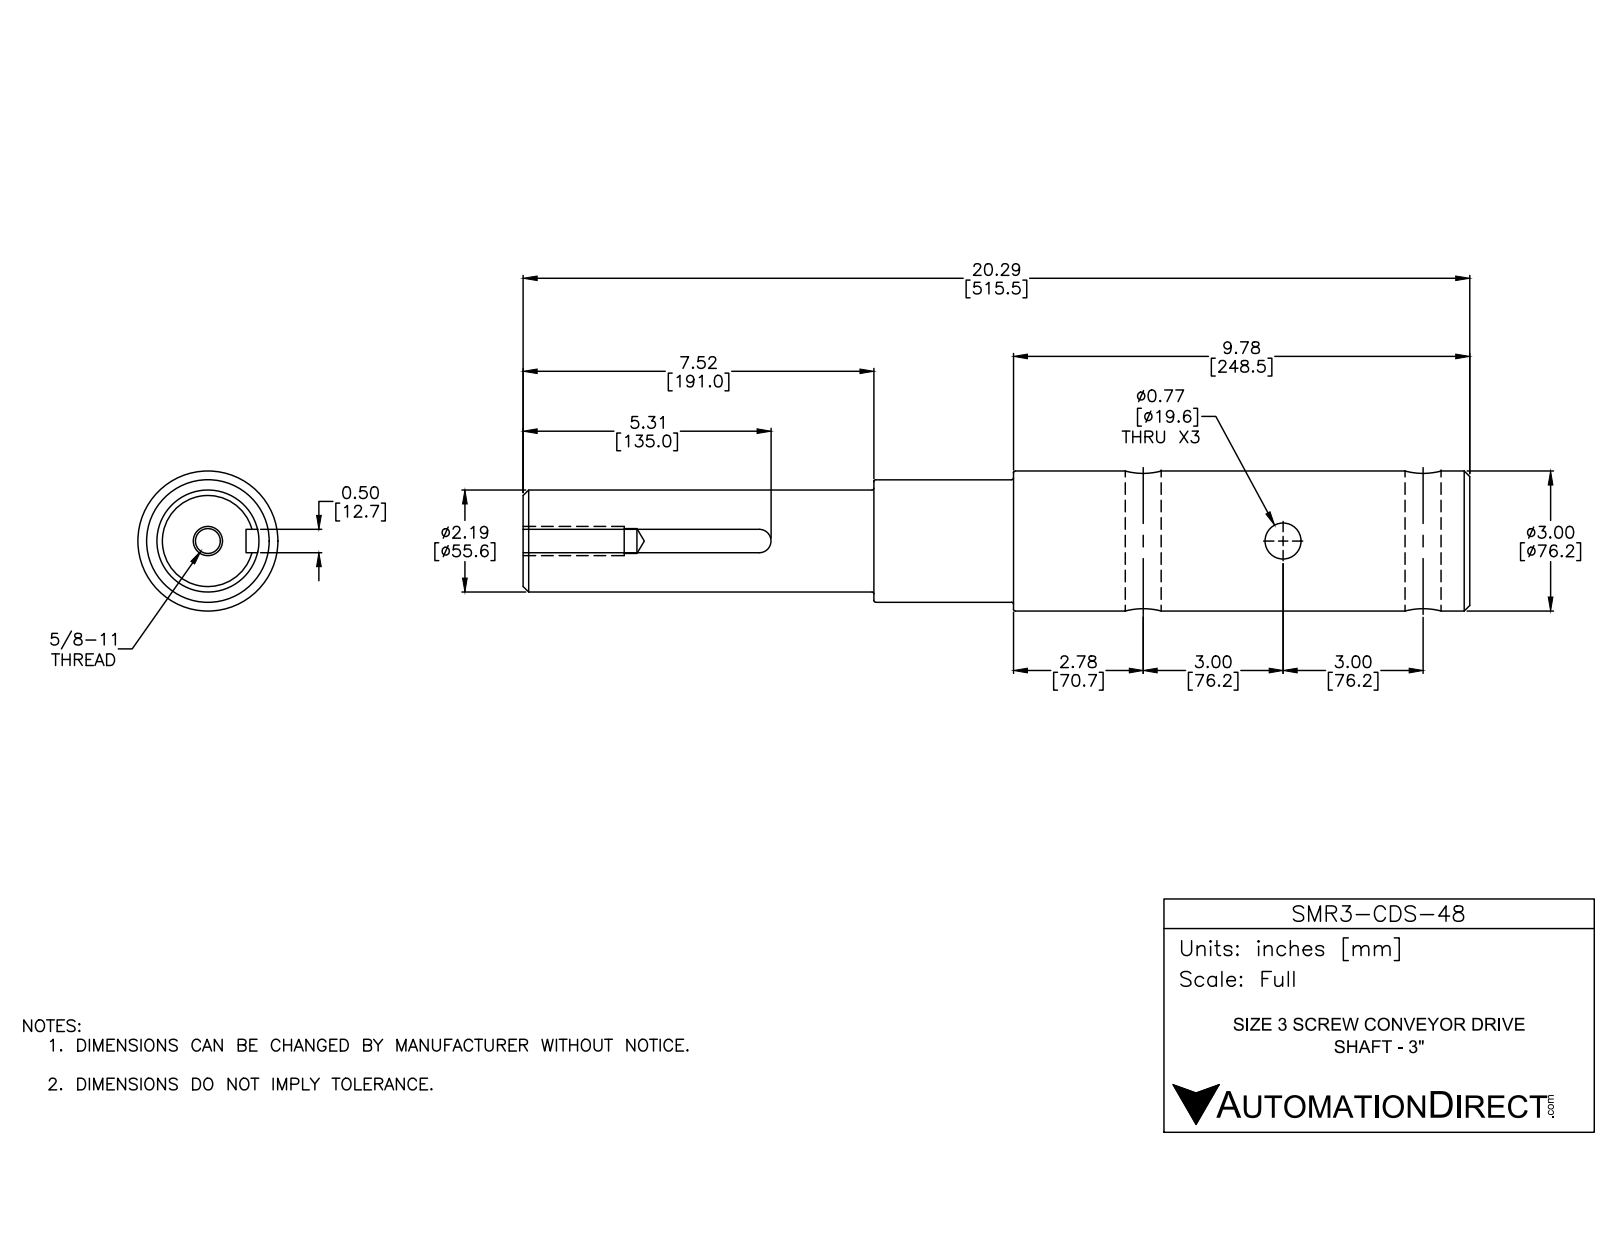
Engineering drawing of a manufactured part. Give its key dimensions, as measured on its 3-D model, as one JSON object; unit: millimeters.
{"part_name": "SMR3-CDS-48", "step_written_by": "SolidWorks 2016 (AUTOMOTIVE_DESIGN)", "units": "millimeters", "bodies": {"solids": 1, "faces": 40, "planar": 8, "cylindrical": 18, "other": 14}, "overall_size": [515.4, 76.2, 76.2], "volume_mm3": 1768000, "surface_area_mm2": 133500, "round_holes": [[19.6, 3], [13.5, 1], [15.9, 1]], "round_bosses_or_shafts": [[76.2, 1], [66.7, 1], [55.5, 1]], "partial_cylinders_radius": [[6.4, 1]], "face_to_face_distances": [515.4, 12.7, 191, 324.5, 267, 76, 248.4, 55, 136, 212], "hole_center_spacings": [152.4]}
